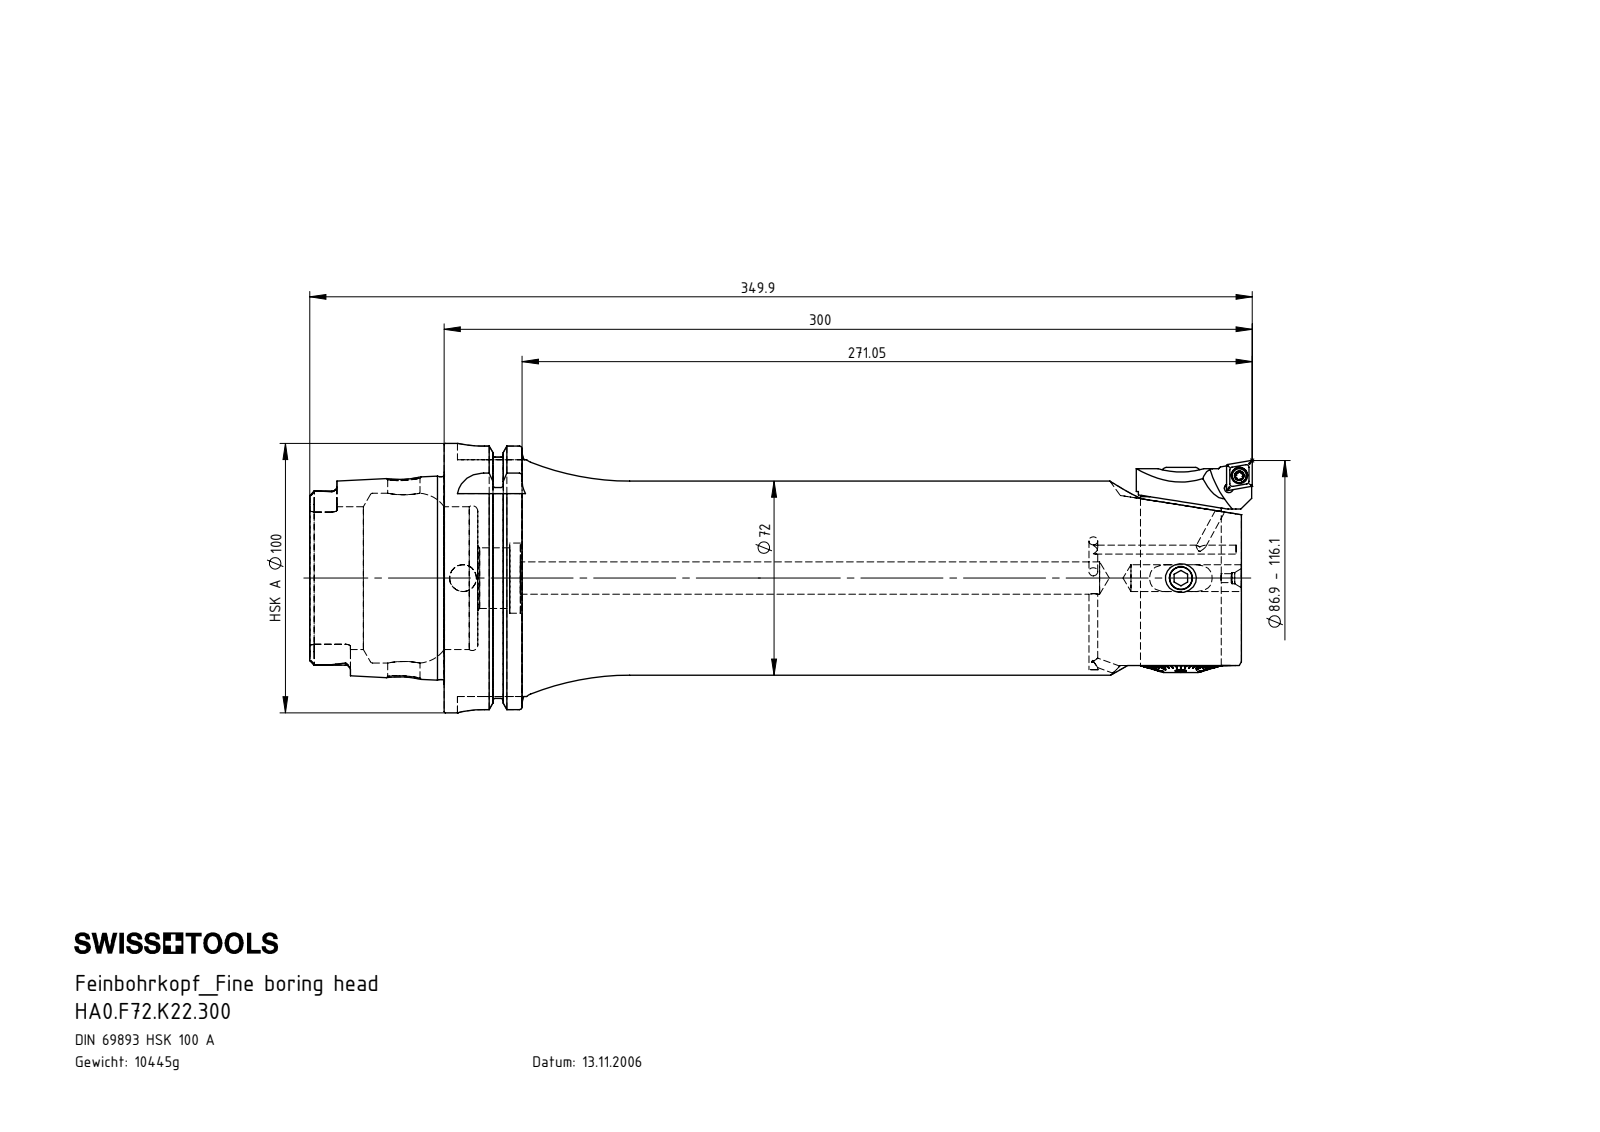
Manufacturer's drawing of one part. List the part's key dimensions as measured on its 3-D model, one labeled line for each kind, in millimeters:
Part name (STEP PRODUCT): ISO 4026 - M10 x 16; A55-BG2.013.005_C; F72-BG2.015.020_B; Klebstoff D10 (+8 more)
STEP written by: SolidWorks 2022 (AUTOMOTIVE_DESIGN)
Units: millimetres
Bodies: 16 solids, 956 faces (368 planar, 207 cylindrical, 381 other)
Overall size (bounding box): 349.9 × 100 × 100
Volume: 1 331 000 mm³ · Surface area: 146 173 mm²
Round holes (diameter × count): ⌀3.3 ×9, ⌀12 ×3, ⌀8.5 ×2, ⌀10 ×2, ⌀4.2 ×1, ⌀4.4 ×1, ⌀5 ×1, ⌀6.1 ×1, ⌀8 ×1, ⌀11 ×1, ⌀11.75 ×1, ⌀12.4 ×1
Round bosses / shafts (diameter × count): ⌀10 ×2, ⌀5.25 ×2, ⌀4 ×2, ⌀100 ×1, ⌀91.95 ×1, ⌀75.26 ×1, ⌀72 ×1, ⌀29.98 ×1
Partial cylindrical surfaces — rounded edges, fillets, slot ends (radius × count): R0.34 ×12, R0.59 ×12, R1.9 ×6, R10 ×6, R0.5 ×4, R4.88 ×4, R3.2 ×3, R1 ×1
Main face-to-face distances: 296, 12.45, 283.55, 49.9, 62.35, 345.9, 6.48, 2.5, 62.28, 76.35
Hole centre spacings: 5.72, 5.86, 14.05, 14.5, 26, 32.5, 256, 266.5
